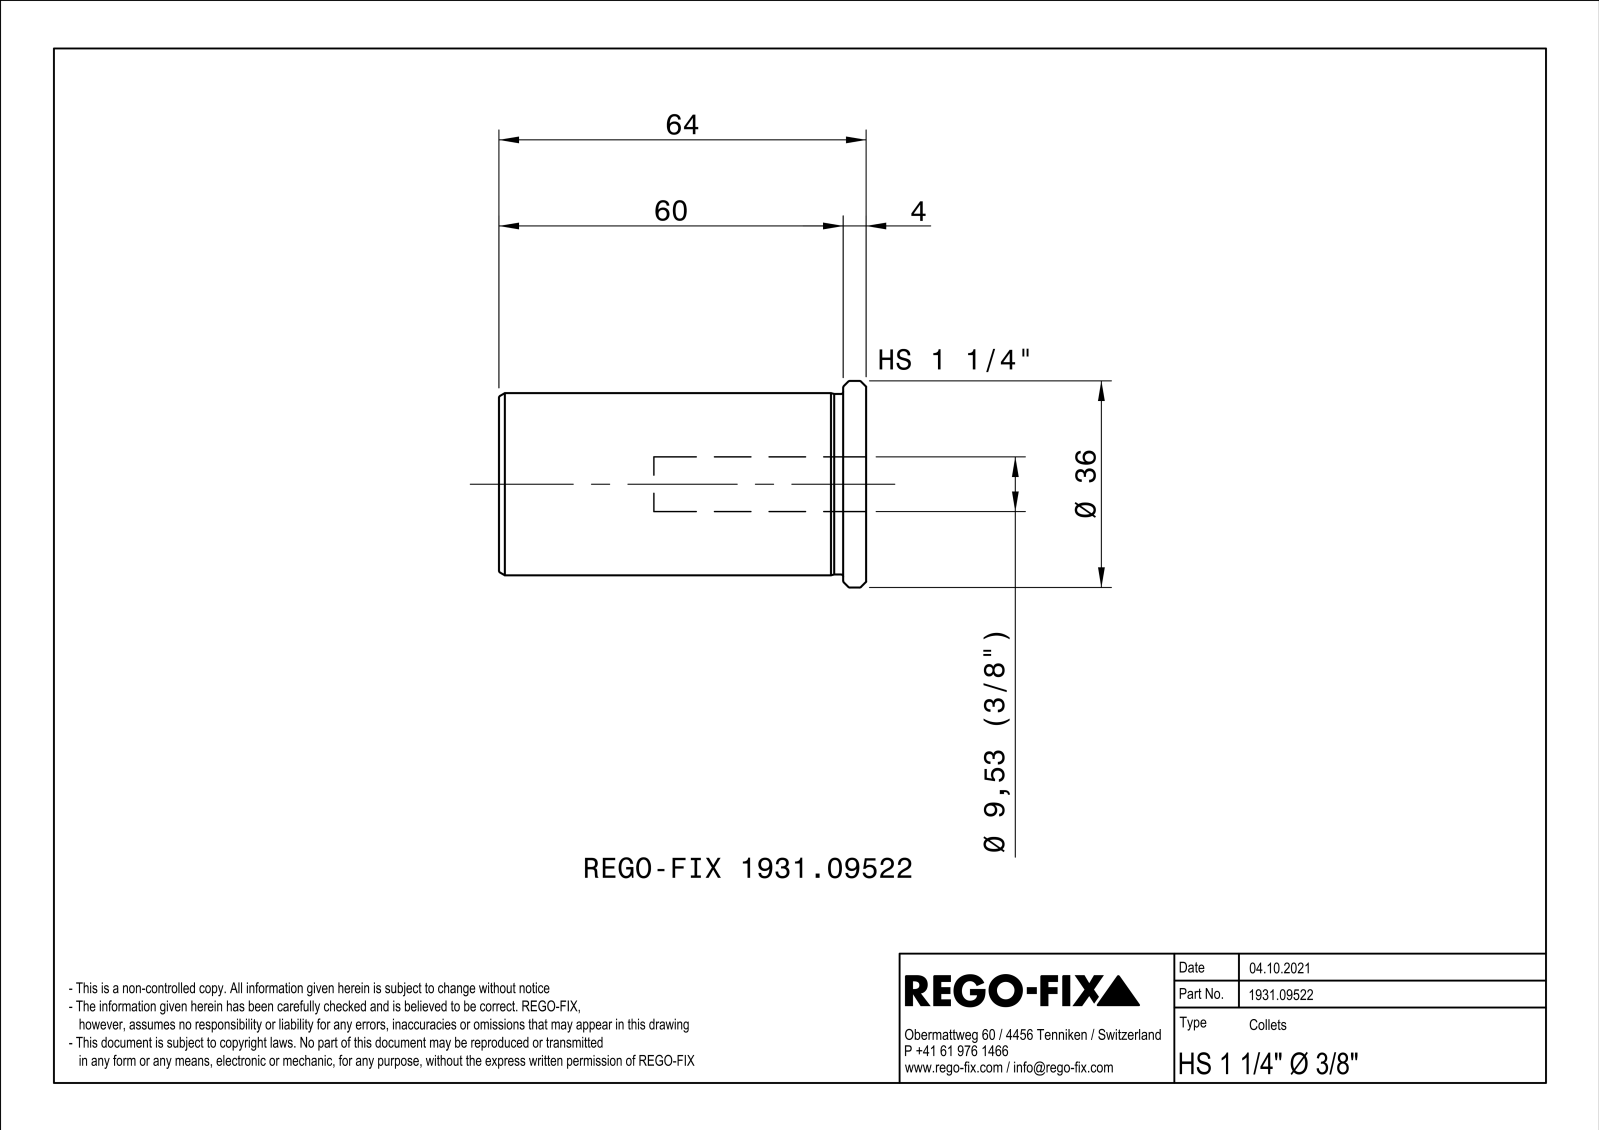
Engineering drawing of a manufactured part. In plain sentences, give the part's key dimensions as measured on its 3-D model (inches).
The part is named "NOCUT". Its 3-D file was written by "SIEMENS PLM Software Solid Edge ST10 (AUTOMOTIVE_DESIGN)". It is 1 solid with 72 faces: 22 planar, 12 cylindrical and 38 other. Overall it measures 2.52 by 1.417 by 1.417 inches. Its volume is 2.294 cubic inches and its surface area 21.39 square inches. Round holes: 1 of diameter 0.375, 1 of diameter 0.394, 1 of diameter 1.043. Round bosses or shafts: 1 of diameter 1.417, 1 of diameter 1.25, 1 of diameter 1.238. The main face-to-face distances are 0.039, 2.52, 0.157, 2.362.
